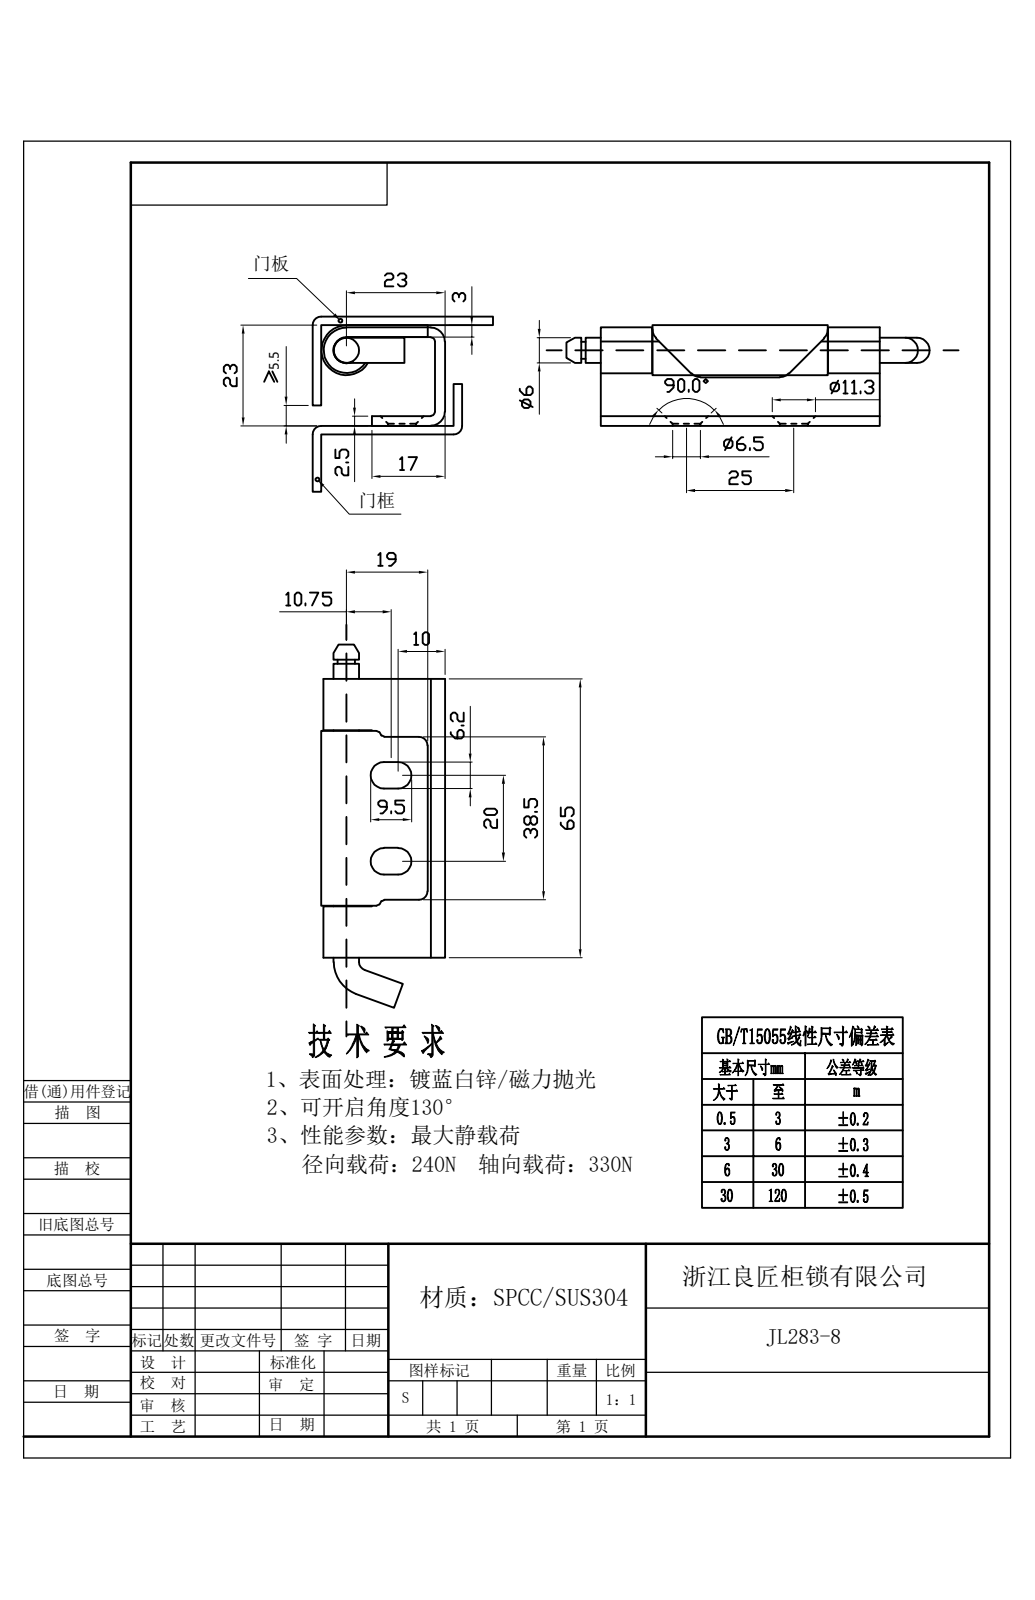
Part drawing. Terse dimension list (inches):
written by: Rhino 8.5 (CONFIG_CONTROL_DESIGN)
unit: in
bodies: 2 solids, 84 faces (36 planar, 36 cylindrical, 12 other)
size: 3.182 × 1.136 × 0.933
volume: 0.377 in³; area: 18.58 in²
holes: 1× ⌀0.24, 1× ⌀0.406
bosses: 2× ⌀0.256, 2× ⌀0.201, 1× ⌀0.461, 1× ⌀0.209, 1× ⌀0.157
rounds: 4× R0.079, 4× R0.118, 4× R0.122, 2× R0.031, 2× R0.13
face distances: 0.098, 0.807, 0.823, 0.724, 0.933, 0.835, 0.11, 0.709, 0.016, 0.126
